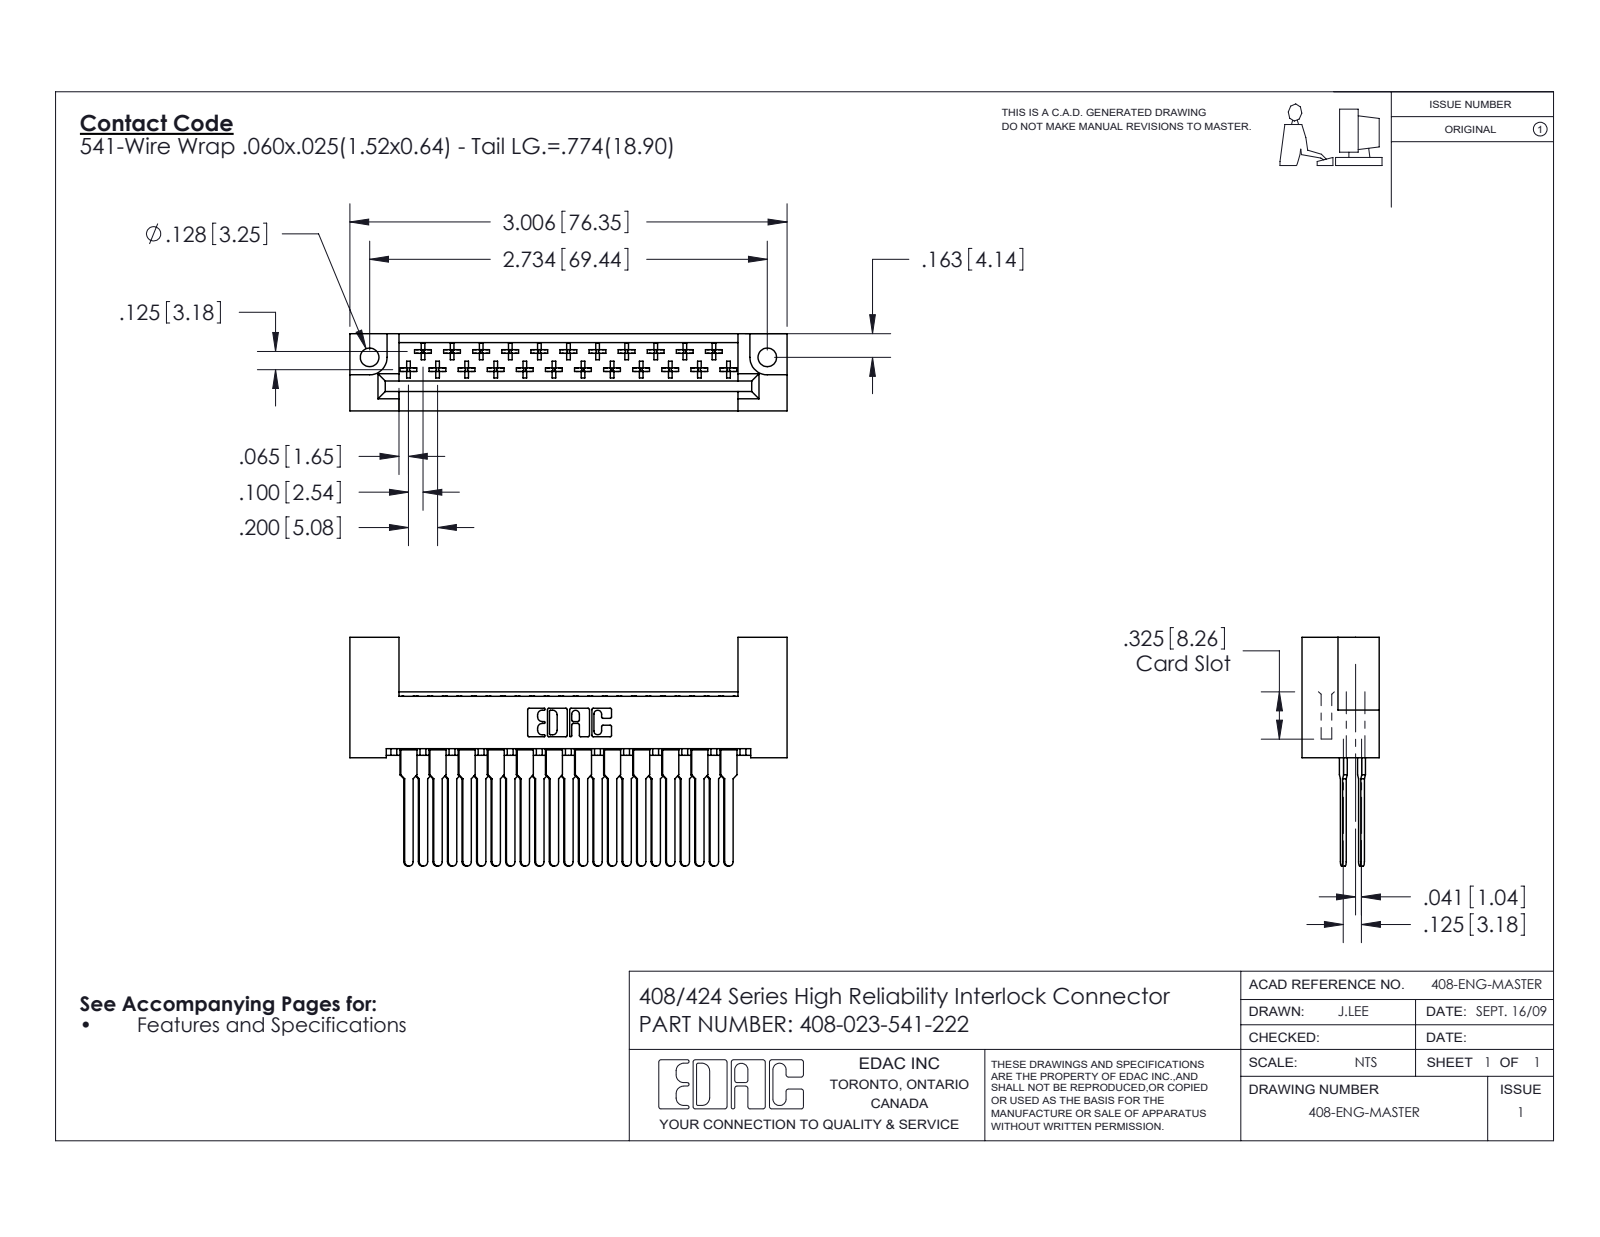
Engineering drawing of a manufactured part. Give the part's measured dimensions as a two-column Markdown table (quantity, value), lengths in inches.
| quantity | value |
| --- | --- |
| part name | 408-023-541-222; 408 Part_023 - 2; 408-290-001_408-290-141 |
| STEP written by | SolidWorks 2016 (CONFIG_CONTROL_DESIGN) |
| units | inches |
| bodies | 24 solids, 1358 faces (1009 planar, 257 cylindrical, 92 other) |
| overall size | 3.006 × 1.572 × 0.531 |
| volume | 0.632 in³ |
| surface area | 19.66 in² |
| round holes (diameter × count) | 0.128 × 2 |
| partial cylindrical surfaces (radius × count) | 0.01 × 138, 0.02 × 25, 0.03 × 23, 0.01 × 22, 0.007 × 6, 0.031 × 6, 0.026 × 3, 0.12 × 2 |
| main face-to-face distances | 0.531, 0.125, 0.1, 0.025, 0.025, 0.104, 0.361, 0.235, 0.259, 0.091 |
| hole center spacings | 2.734 |
